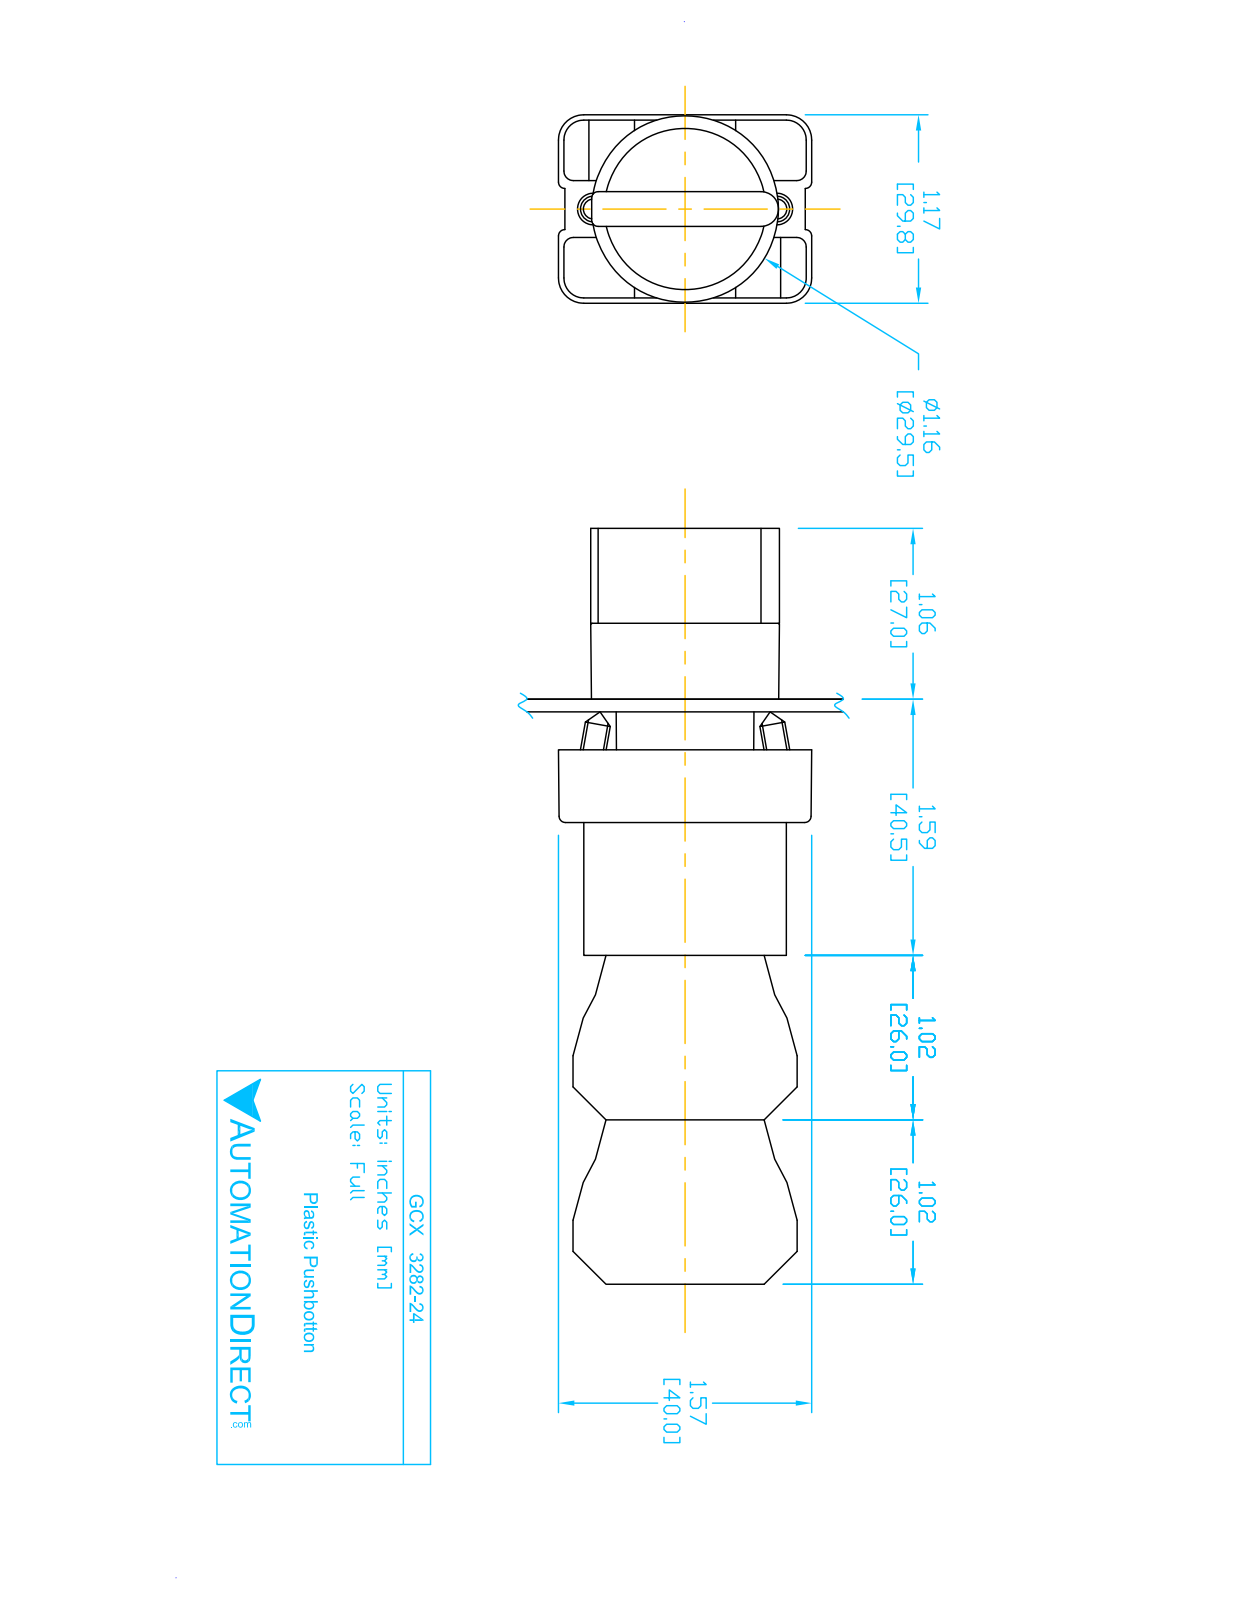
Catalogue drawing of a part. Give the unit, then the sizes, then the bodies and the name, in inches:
Units: inches
Overall size (bounding box): 4.677 × 1.581 × 1.177
Round holes (diameter × count): ⌀0.079 ×4, ⌀0.087 ×2, ⌀0.124 ×2, ⌀0.13 ×2, ⌀0.197 ×1, ⌀0.469 ×1, ⌀0.878 ×1, ⌀0.888 ×1, ⌀1.024 ×1
Round bosses / shafts (diameter × count): ⌀0.157 ×4, ⌀1.175 ×1, ⌀1.004 ×1, ⌀0.945 ×1, ⌀0.856 ×1, ⌀0.78 ×1, ⌀0.504 ×1
Partial cylindrical surfaces — rounded edges, fillets, slot ends (radius × count): R0.059 ×24, R0.041 ×12, R0.124 ×12, R0.157 ×12, R0.039 ×9, R0.02 ×2, R0.063 ×2, R0.079 ×2
Main face-to-face distances: 0.579, 0.593, 1.024, 1.171, 0.014, 0.827, 1.85, 3.043, 2.02, 1.193
Hole centre spacings: 0.236, 1.003, 0.974, 0.472, 0.539, 0.544, 1.083, 0.484
Volume: 4.751 in³ · Surface area: 59.22 in²
Bodies: 11 solids, 724 faces (488 planar, 193 cylindrical, 43 other)
Part name (STEP PRODUCT): ECX1050; ecx1030; GCX3282-24; ecx1040 (+2 more)
STEP written by: SolidWorks 2016 (AUTOMOTIVE_DESIGN)
